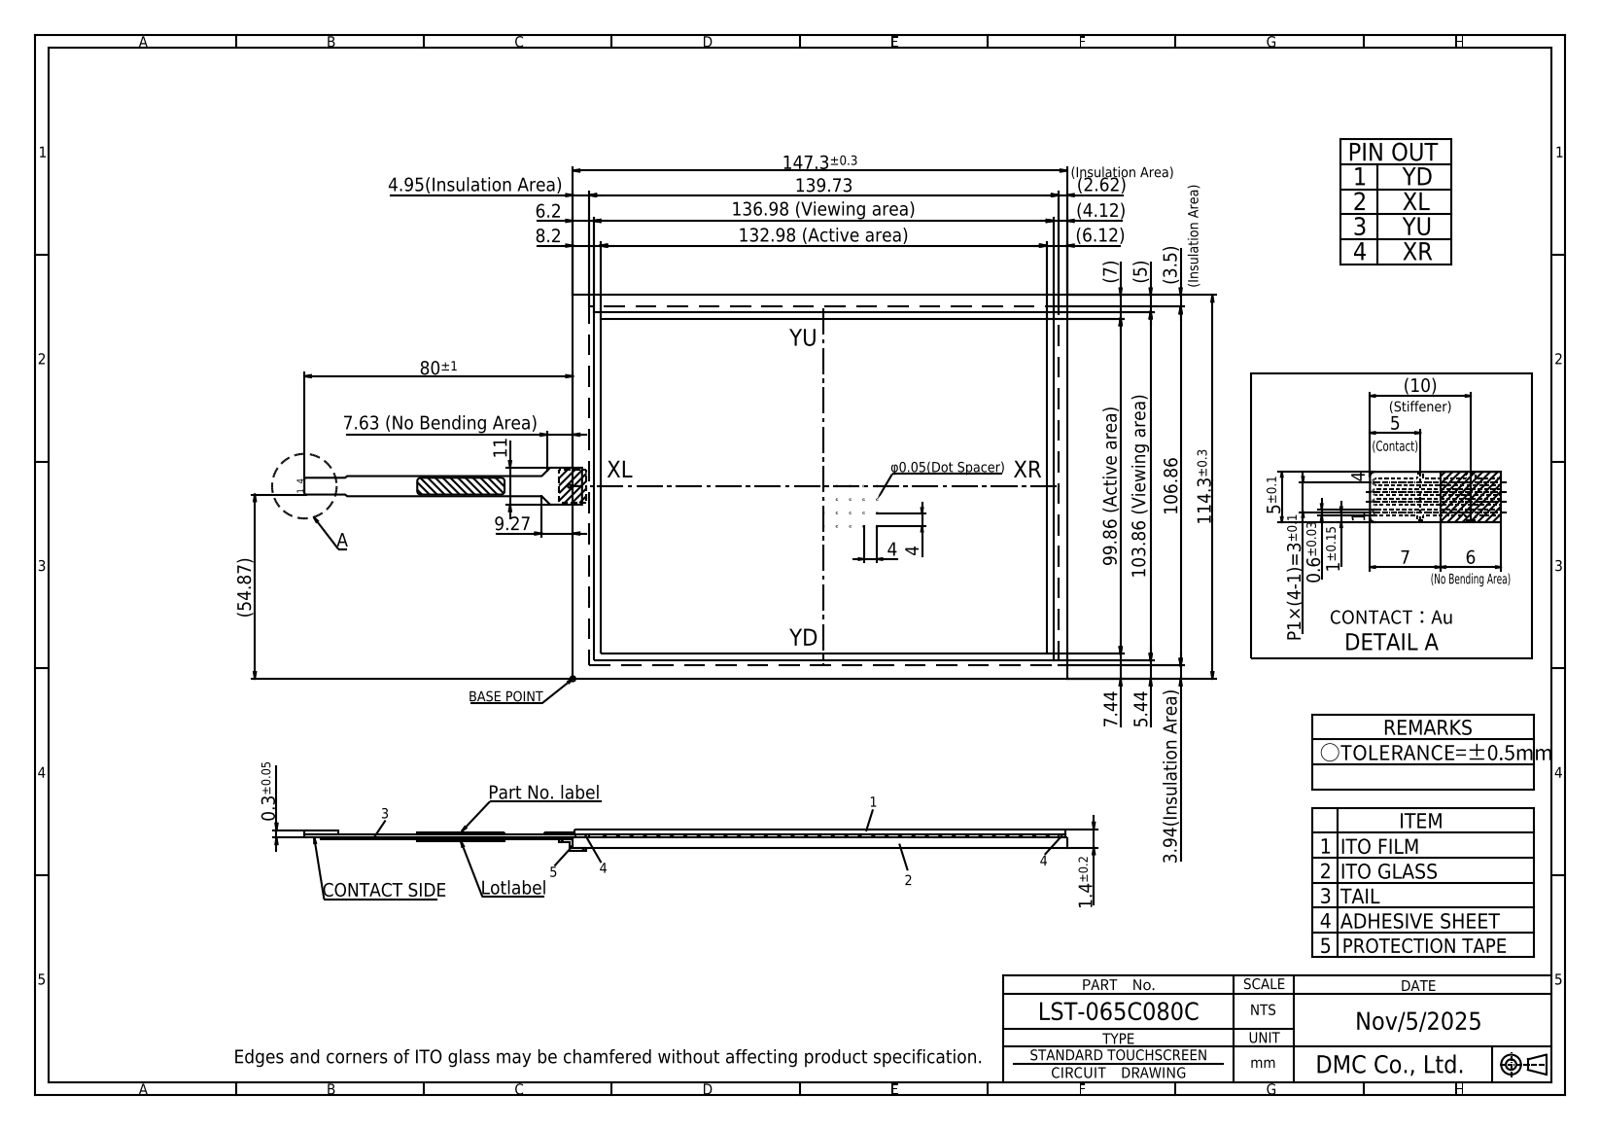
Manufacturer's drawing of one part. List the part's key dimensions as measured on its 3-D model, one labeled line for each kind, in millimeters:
Part name (STEP PRODUCT): LST-065C080C
STEP written by: Autodesk Inventor 2020 (CONFIG_CONTROL_DESIGN)
Units: millimetres
Bodies: 2 solids, 52 faces (46 planar, 6 cylindrical, 0 other)
Overall size (bounding box): 227.3 × 114.3 × 2.6
Volume: 35 324 mm³ · Surface area: 35 900 mm²
Partial cylindrical surfaces — rounded edges, fillets, slot ends (radius × count): R0.3 ×4, R0.5 ×2
Main face-to-face distances: 2.1, 2, 2.2, 2.3, 114.3, 147.3, 0.5, 0.6, 0.4, 2.6
